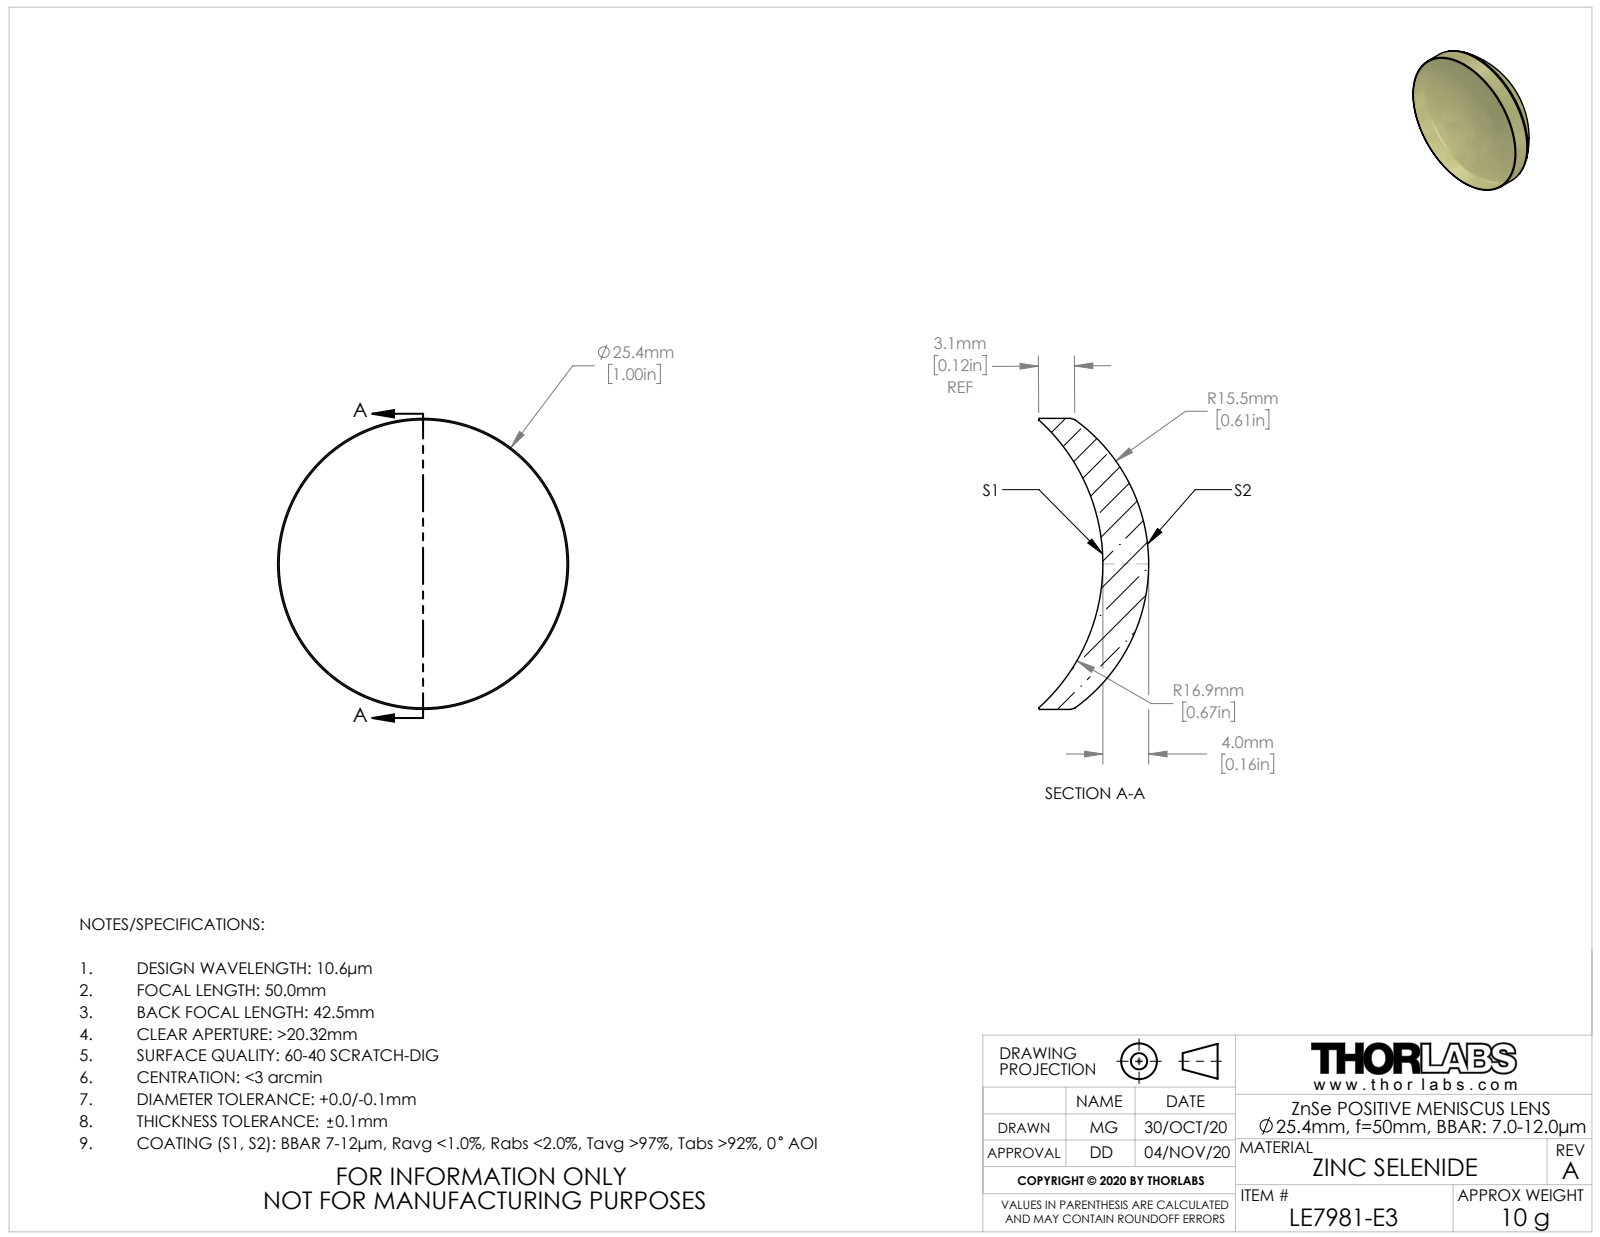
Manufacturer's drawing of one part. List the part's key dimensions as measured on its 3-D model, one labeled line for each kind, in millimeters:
Part name (STEP PRODUCT): TTN225628-E0W
STEP written by: SolidWorks 2018 (CONFIG_CONTROL_DESIGN)
Units: millimetres
Bodies: 1 solid, 10 faces (0 planar, 2 cylindrical, 8 other)
Overall size (bounding box): 25.4 × 25.4 × 9.6
Volume: 1 858 mm³ · Surface area: 1 483 mm²
Round bosses / shafts (diameter × count): ⌀25.4 ×1
